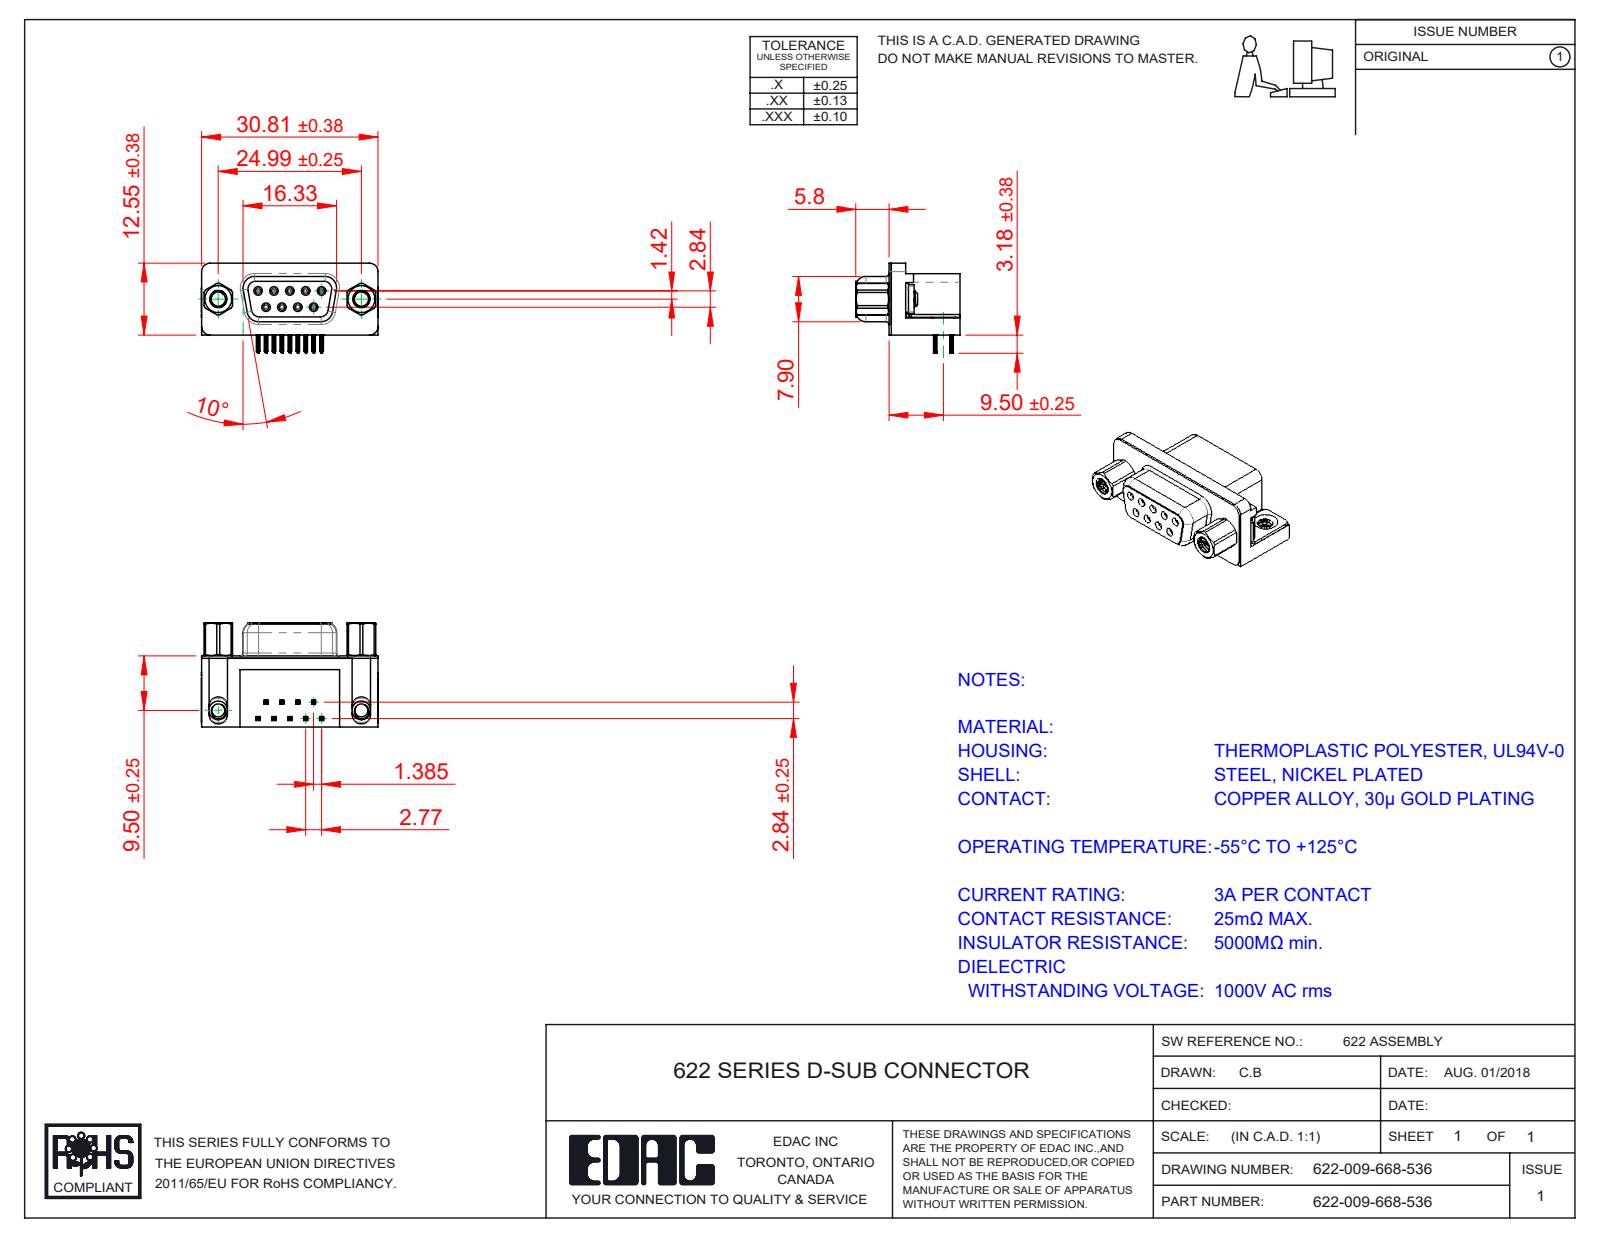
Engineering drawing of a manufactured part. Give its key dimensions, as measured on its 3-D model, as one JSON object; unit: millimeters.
{"part_name": "622 Contact Top; 622-009-668-536; 622 M3 Threaded Rivet; 622 Socket Bottom (+3 more)", "step_written_by": "SolidWorks 2016 (CONFIG_CONTROL_DESIGN)", "units": "millimeters", "bodies": {"solids": 15, "faces": 1612, "planar": 716, "cylindrical": 428, "other": 468}, "overall_size": [30.89, 18.2, 16.25], "volume_mm3": 3720, "surface_area_mm2": 5082, "round_holes": [[0.8, 9], [0.9, 9], [2.5, 2], [4, 2], [4.8, 2], [5, 2]], "round_bosses_or_shafts": [[1.2, 9], [4.9, 2], [4.75, 2], [3.9, 2]], "partial_cylinders_radius": [[0.1, 72], [0.15, 36], [0.35, 18], [1, 18], [0.5, 10], [0.34, 9], [0.25, 8], [1.35, 8]], "face_to_face_distances": [0.4, 12, 12.4, 0.35, 2.9, 2.5, 6.2, 10.34, 0.5, 9.5], "hole_center_spacings": [3.16, 2.77, 5.54, 5.03, 5.04, 8.31, 7.48, 7.49]}
